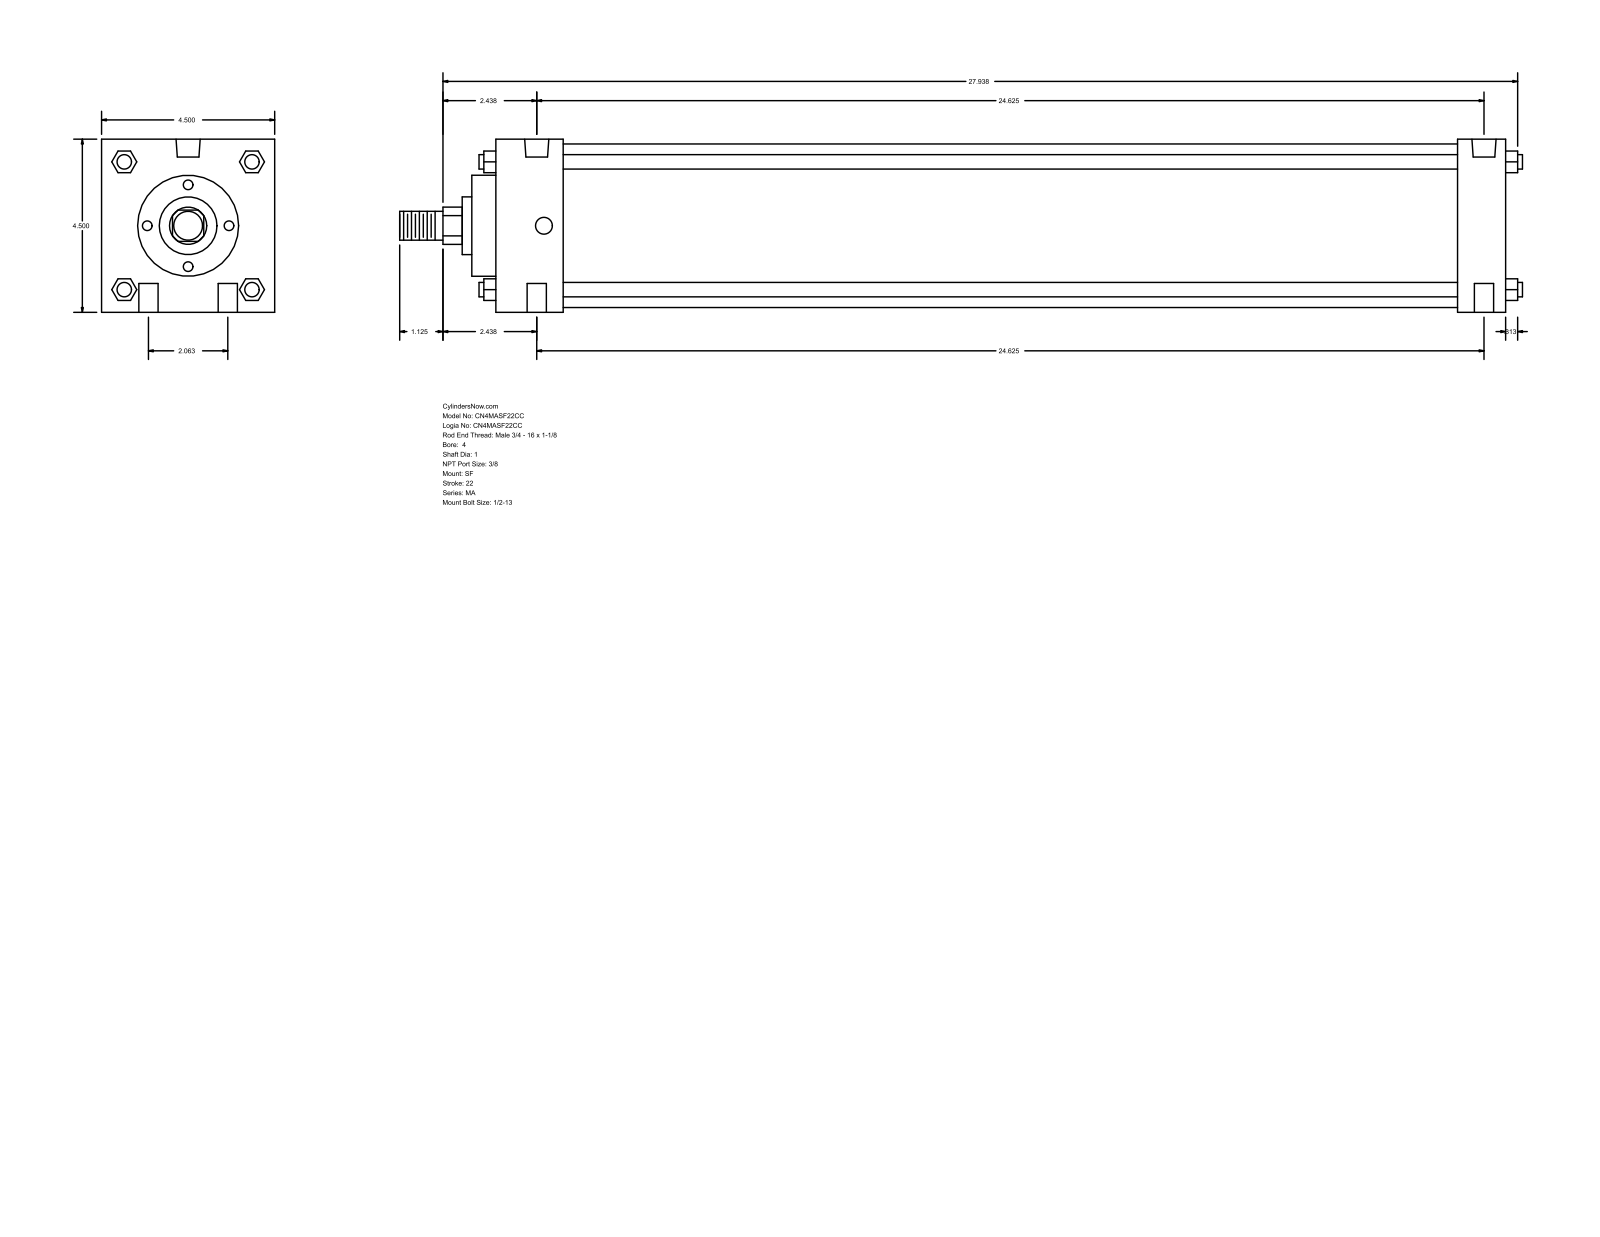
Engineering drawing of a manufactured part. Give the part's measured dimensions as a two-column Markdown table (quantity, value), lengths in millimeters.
| quantity | value |
| --- | --- |
| part name | MA_SF__0400_1 |
| STEP written by | GSSL Pune (CONFIG_CONTROL_DESIGN) |
| units | millimeters |
| bodies | 0 solids, 126 faces (95 planar, 31 cylindrical, 0 other) |
| overall size | 741.36 × 114.3 × 114.3 |
| round holes (diameter × count) | 12.7 × 4, 11.11 × 2, 15.93 × 2 |
| round bosses / shafts (diameter × count) | 9.53 × 4, 107.95 × 1, 66.67 × 1, 38.1 × 1, 25.4 × 1, 19.05 × 1 |
| partial cylindrical surfaces (radius × count) | 12.29 × 1 |
| main face-to-face distances | 114.3, 666.75, 635, 31.75, 44.46, 590.54, 622.29, 682.62, 15.87, 60.33 |
| hole center spacings | 26.19, 626.03, 625.48, 52.38, 627.67, 615.95 |
